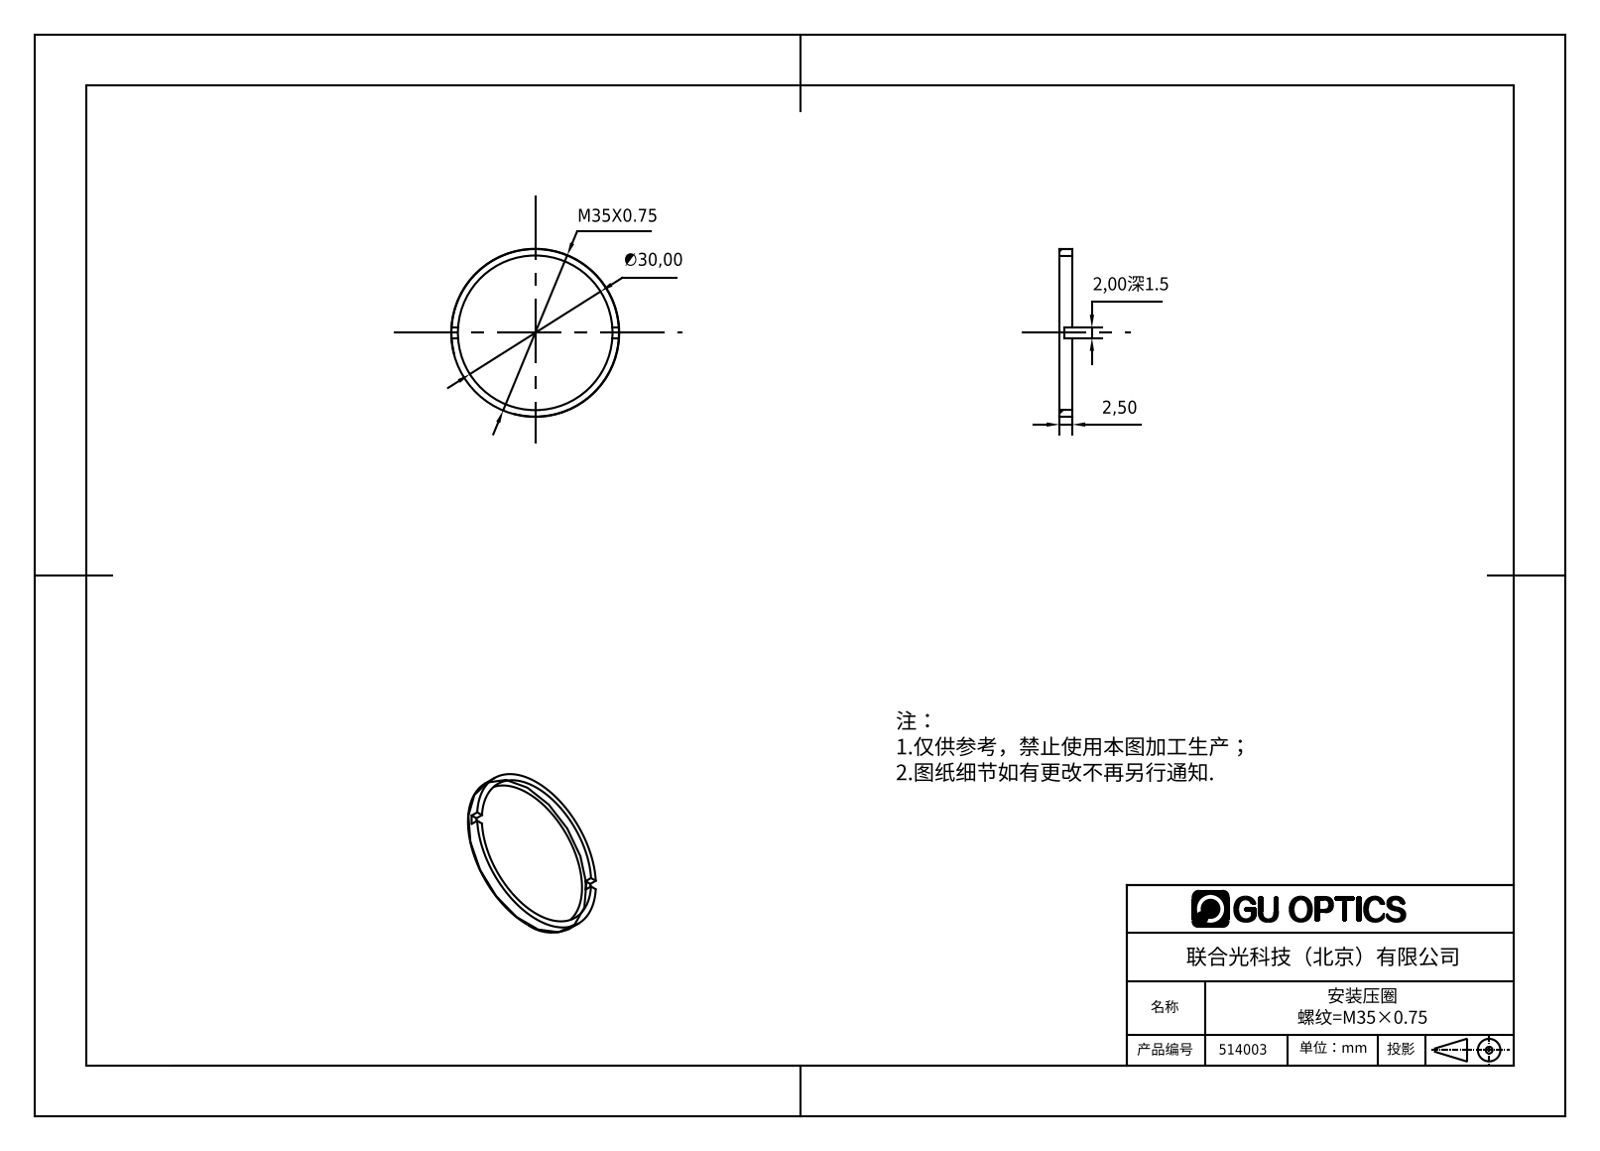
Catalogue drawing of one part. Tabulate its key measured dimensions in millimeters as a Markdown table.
| quantity | value |
| --- | --- |
| part name | 514004 |
| STEP written by | SolidWorks 2016 (AUTOMOTIVE_DESIGN) |
| units | millimeters |
| bodies | 1 solid, 13 faces (9 planar, 4 cylindrical, 0 other) |
| overall size | 32.6 × 32.6 × 2.5 |
| volume | 312 mm³ |
| surface area | 743 mm² |
| round holes (diameter × count) | 30 × 1 |
| round bosses / shafts (diameter × count) | 32.6 × 1 |
| main face-to-face distances | 2.5, 1, 1.5, 2 |
